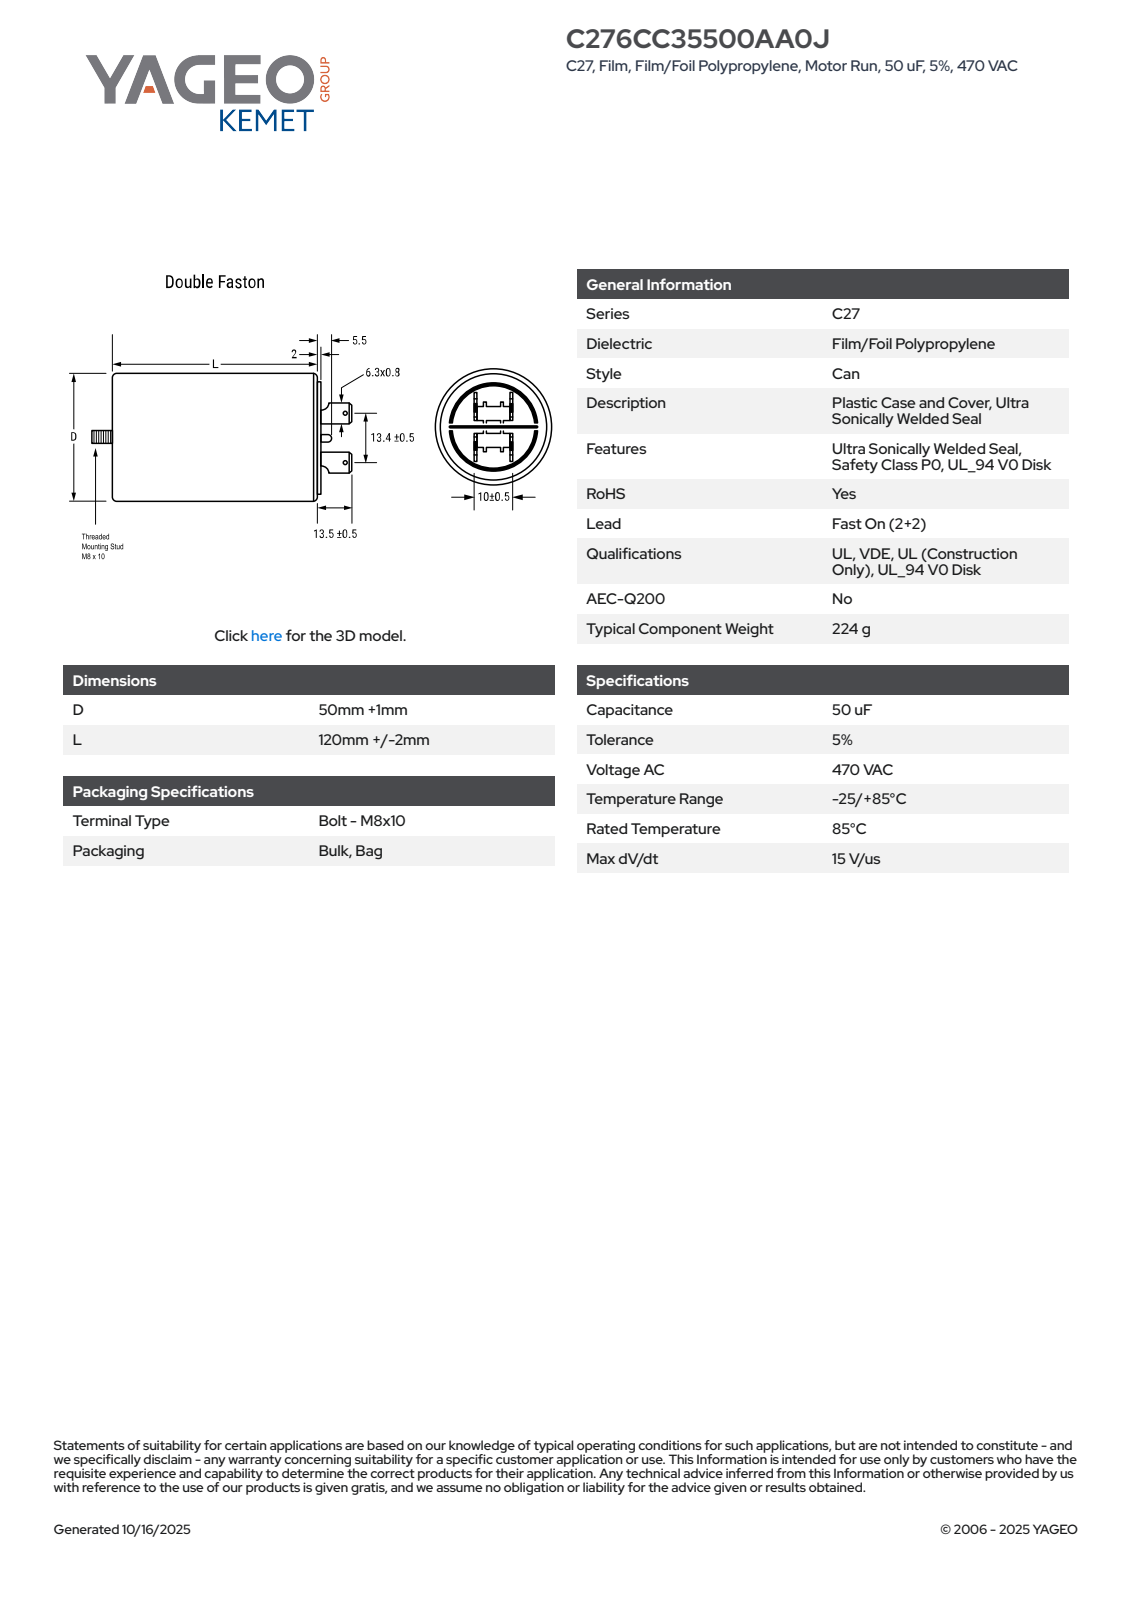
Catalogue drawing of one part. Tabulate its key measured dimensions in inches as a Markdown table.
| quantity | value |
| --- | --- |
| part name | CFM_C27DF_50X120_D51L122 |
| STEP written by | SolidWorks 2014 (AUTOMOTIVE_DESIGN) |
| units | inches |
| bodies | 1 solid, 137 faces (49 planar, 53 cylindrical, 35 other) |
| overall size | 5.748 × 2.008 × 2.008 |
| volume | 15.39 in³ |
| surface area | 38.41 in² |
| round holes (diameter × count) | 0.047 × 2 |
| round bosses / shafts (diameter × count) | 2.008 × 1, 1.544 × 1, 0.315 × 1 |
| partial cylindrical surfaces (radius × count) | 0.01 × 9, 0.157 × 2, 1.004 × 1 |
| main face-to-face distances | 4.882, 4.803, 0.079, 0.031, 0.382, 0.35, 0.413, 0.02, 0.394, 5.197 |
| hole center spacings | 0.547 |
